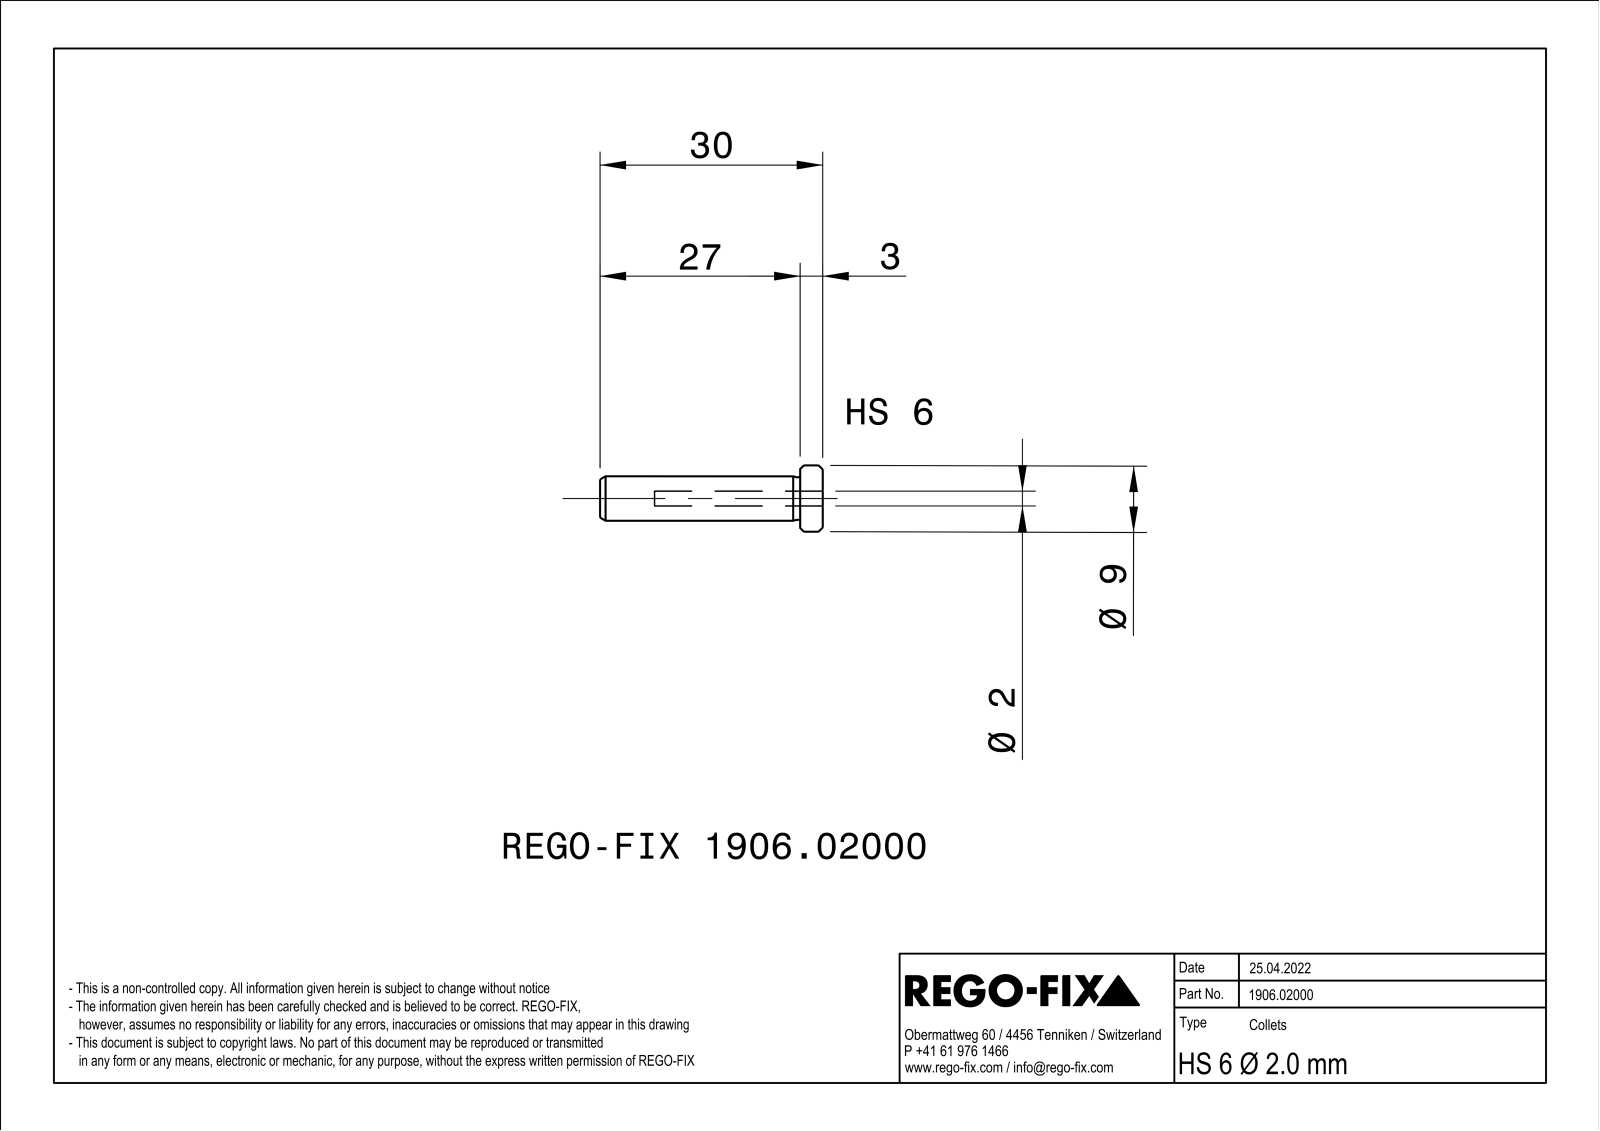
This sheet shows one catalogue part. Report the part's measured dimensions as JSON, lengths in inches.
{"part_name": "NOCUT", "step_written_by": "SIEMENS PLM Software Solid Edge ST10 (AUTOMOTIVE_DESIGN)", "units": "inches", "bodies": {"solids": 1, "faces": 67, "planar": 14, "cylindrical": 9, "other": 44}, "overall_size": [1.181, 0.352, 0.352], "volume_in3": 0.045, "surface_area_in2": 1.758, "round_holes": [[0.079, 1], [0.138, 1]], "round_bosses_or_shafts": [[0.352, 1], [0.236, 1], [0.226, 1]], "face_to_face_distances": [0.018, 0.018, 0.118, 1.181, 1.063, 0.114, 1.067]}
